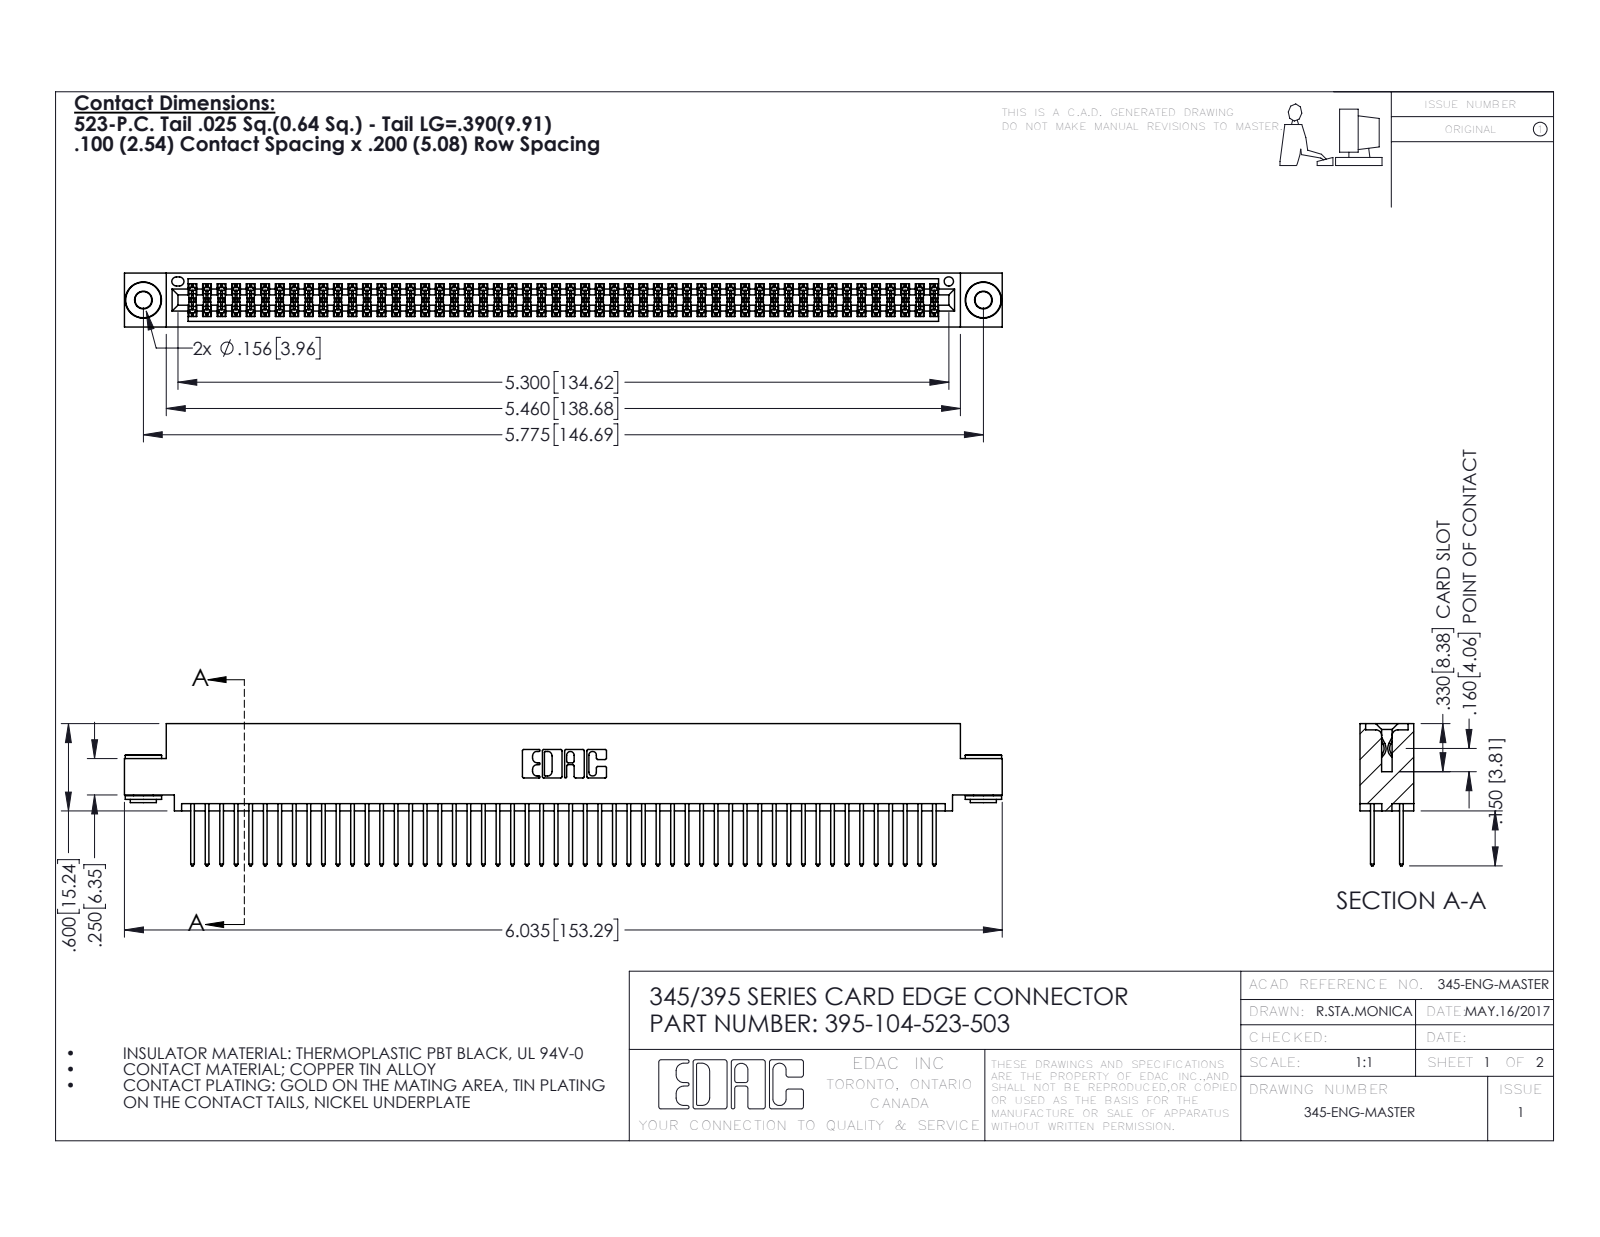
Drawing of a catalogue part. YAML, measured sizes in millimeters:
part_name: "345-250-002_345-250-002-102; 345-292-001_345-293-123; 345 Part_0.110 Offset - 0.156 Dia-TH; 395-104-523-503"
step_written_by: "SolidWorks 2016 (CONFIG_CONTROL_DESIGN)"
units: millimeters
bodies: {solids: 107, faces: 5368, planar: 3526, cylindrical: 1834, other: 8}
overall_size: [153.3, 24.8, 9.4]
volume: 15100
surface_area: 23830
round_holes:
  - {diameter: 2.9, count: 2}
  - {diameter: 4, count: 2}
  - {diameter: 1.6, count: 1}
round_bosses_or_shafts:
  - {diameter: 6.4, count: 2}
  - {diameter: 4.6, count: 2}
  - {diameter: 3.5, count: 2}
partial_cylinders:
  - {radius: 0.2, count: 156}
  - {radius: 0.3, count: 104}
  - {radius: 0.3, count: 22}
  - {radius: 0.2, count: 6}
  - {radius: 0.8, count: 6}
  - {radius: 0.7, count: 3}
  - {radius: 0.4, count: 2}
  - {radius: 0.5, count: 2}
face_to_face_distances: [1.8, 7.6, 5.1, 0.6, 2.5, 6.9, 9.4, 5.7, 4.4, 3.8]
hole_center_spacings: [6.9, 140.7, 146.7]
